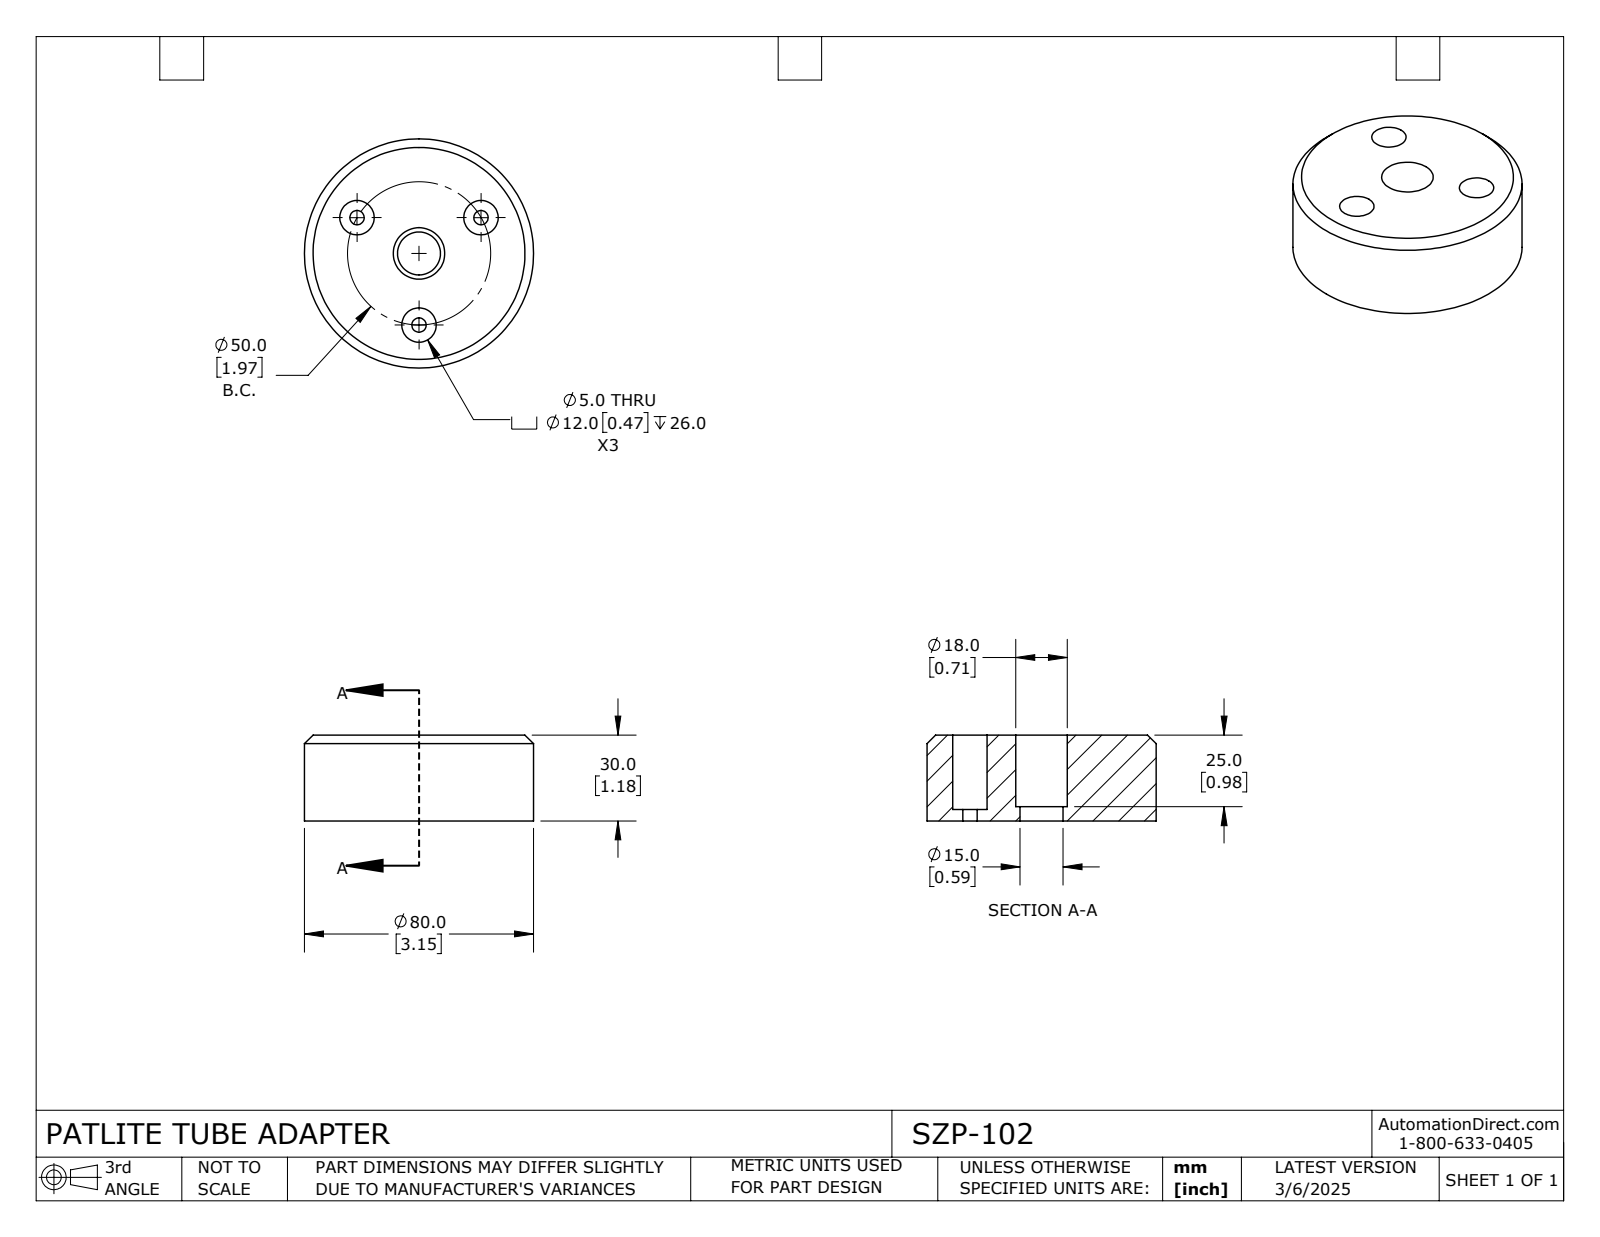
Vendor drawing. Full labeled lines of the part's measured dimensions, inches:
Part name (STEP PRODUCT): SZP-102
STEP written by: SolidWorks 2024 (CONFIG_CONTROL_DESIGN)
Units: inches
Bodies: 1 solid, 32 faces (8 planar, 22 cylindrical, 2 other)
Overall size (bounding box): 3.15 × 3.15 × 1.181
Volume: 8.108 in³ · Surface area: 34.13 in²
Round holes (diameter × count): ⌀0.197 ×3, ⌀0.472 ×3, ⌀0.13 ×1, ⌀0.157 ×1, ⌀0.591 ×1, ⌀0.709 ×1
Round bosses / shafts (diameter × count): ⌀3.15 ×1
Main face-to-face distances: 1.181, 0.157, 1.024, 0.197, 0.984, 0.039, 0.827, 0.787
Hole centre spacings: 0.984, 1.705, 0.515, 0.699, 1.207, 1.628, 1.398
